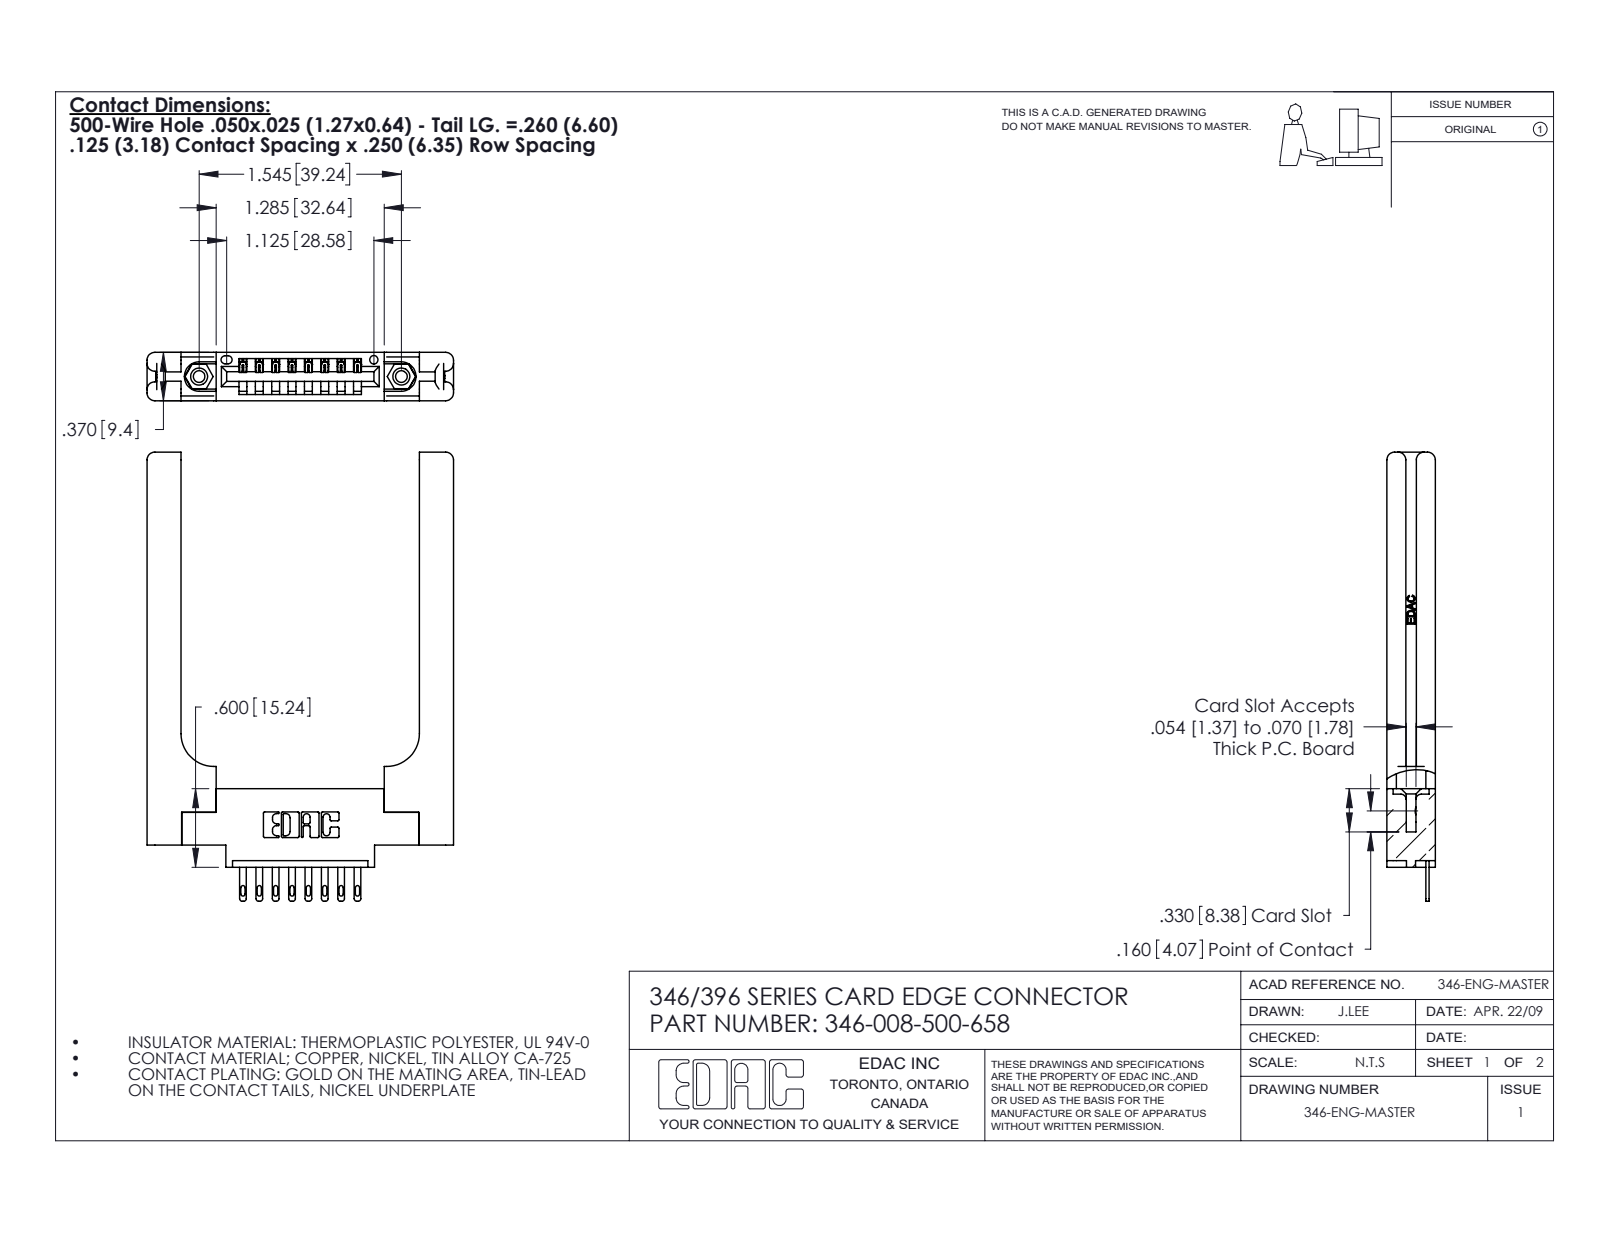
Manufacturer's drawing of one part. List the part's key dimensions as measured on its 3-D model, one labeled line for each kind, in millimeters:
Part name (STEP PRODUCT): 345-250-001_345-250-001-102; 345-292-001_345-293-100; 346 Part_0.170 Offset - 0.156 Dia-TH; 346-220-058_345-220-058 (+1 more)
STEP written by: SolidWorks 2020 (CONFIG_CONTROL_DESIGN)
Units: millimetres
Bodies: 13 solids, 828 faces (514 planar, 254 cylindrical, 60 other)
Overall size (bounding box): 87.1 × 59.5 × 9.4
Volume: 12 800 mm³ · Surface area: 11 630 mm²
Round holes (diameter × count): ⌀2.3 ×2, ⌀3.2 ×2, ⌀4 ×2, ⌀1.6 ×1
Round bosses / shafts (diameter × count): ⌀3.9 ×2
Partial cylindrical surfaces — rounded edges, fillets, slot ends (radius × count): R0.3 ×22, R0.2 ×16, R0.4 ×16, R0.5 ×16, R1.5 ×16, R0.2 ×6, R0.8 ×6, R0.7 ×3
Main face-to-face distances: 9.4, 3.8, 5.6, 1.8, 3.8, 2.6, 1.2, 8.2, 4.4, 6.4
Hole centre spacings: 6.2, 34.1, 39.2
